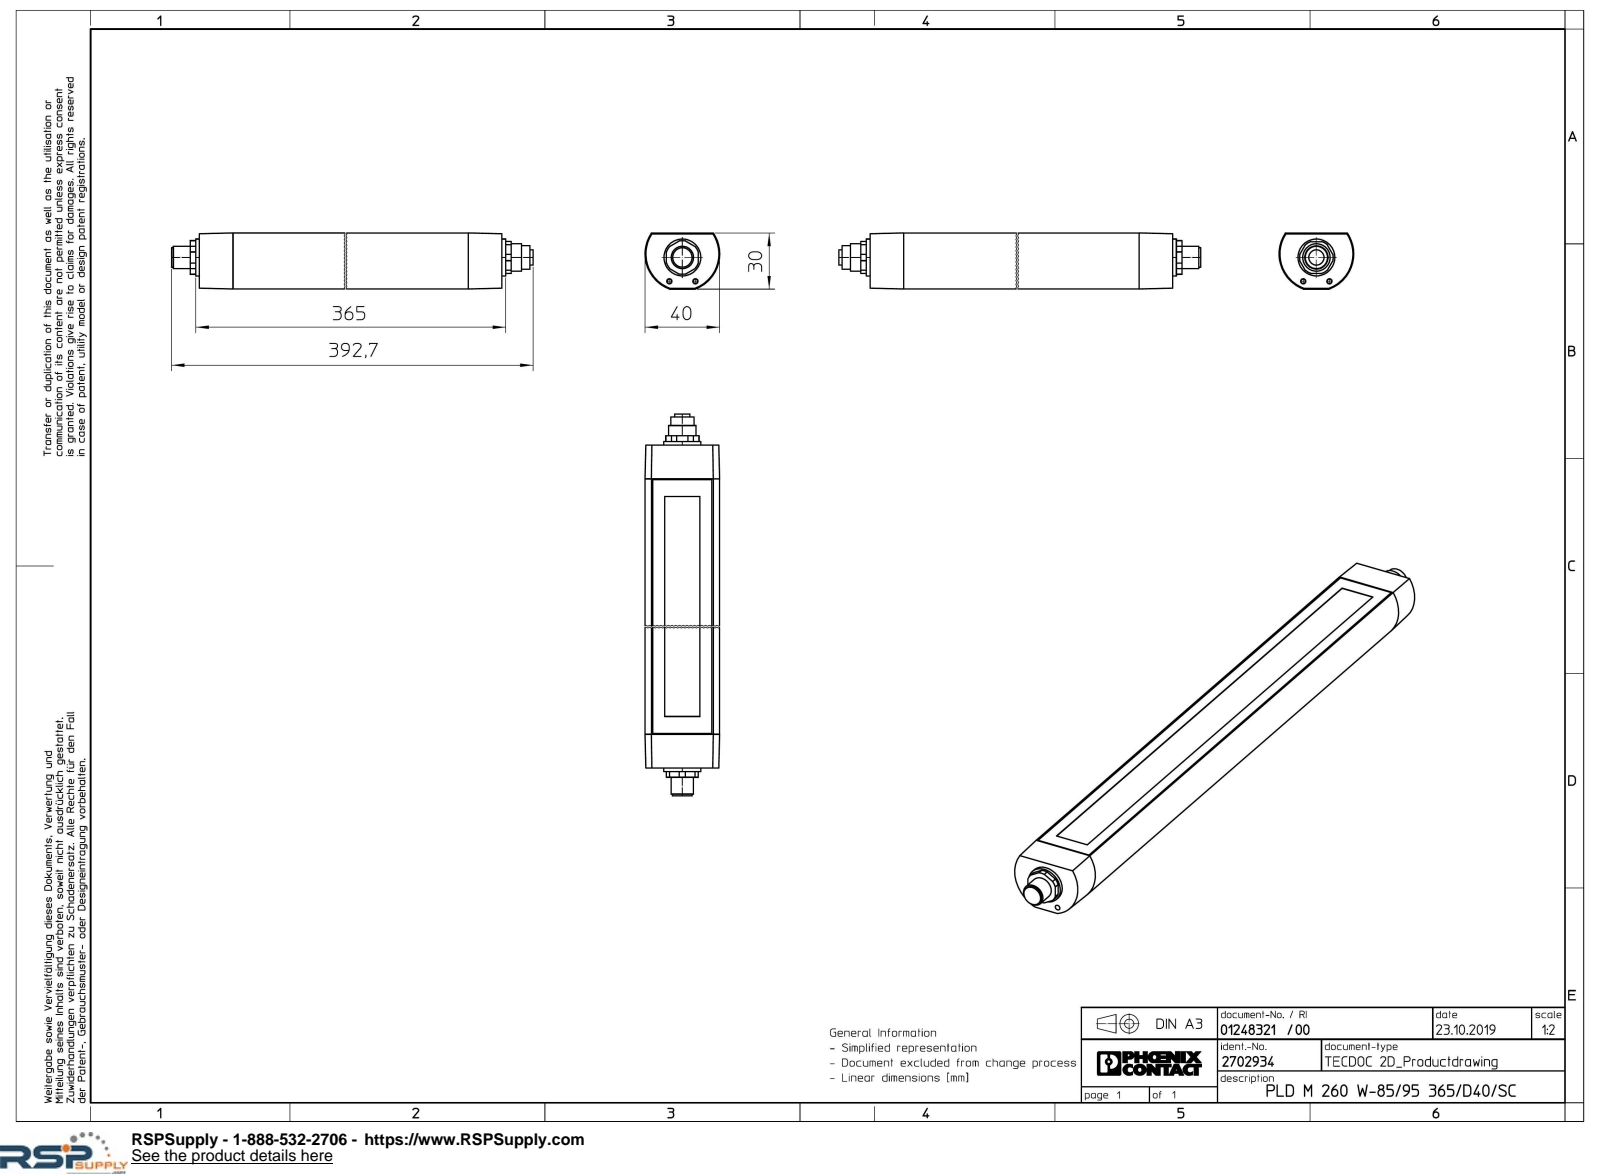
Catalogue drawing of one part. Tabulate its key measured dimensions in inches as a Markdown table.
| quantity | value |
| --- | --- |
| part name | PLD_M_260_W_85_95_365_D40_SC-select |
| STEP written by | Creo Elements/Direct Modeling 20.1A 29-Sep-2018 (C) Parametric Technology GmbH (AUTOMOTIVE_DESIGN) |
| units | inches |
| bodies | 1 solid, 86 faces (44 planar, 30 cylindrical, 12 other) |
| overall size | 15.461 × 1.575 × 1.179 |
| volume | 23.03 in³ |
| surface area | 73.86 in² |
| round holes (diameter × count) | 0.472 × 1 |
| round bosses / shafts (diameter × count) | 0.778 × 1, 0.579 × 1, 0.492 × 1, 0.409 × 1, 0.323 × 1 |
| partial cylindrical surfaces (radius × count) | 0.354 × 1, 0.787 × 1 |
| main face-to-face distances | 1.171, 1.175, 14.213, 1.179, 1.485, 1.486, 0.197, 14.409, 0.118, 14.488 |
